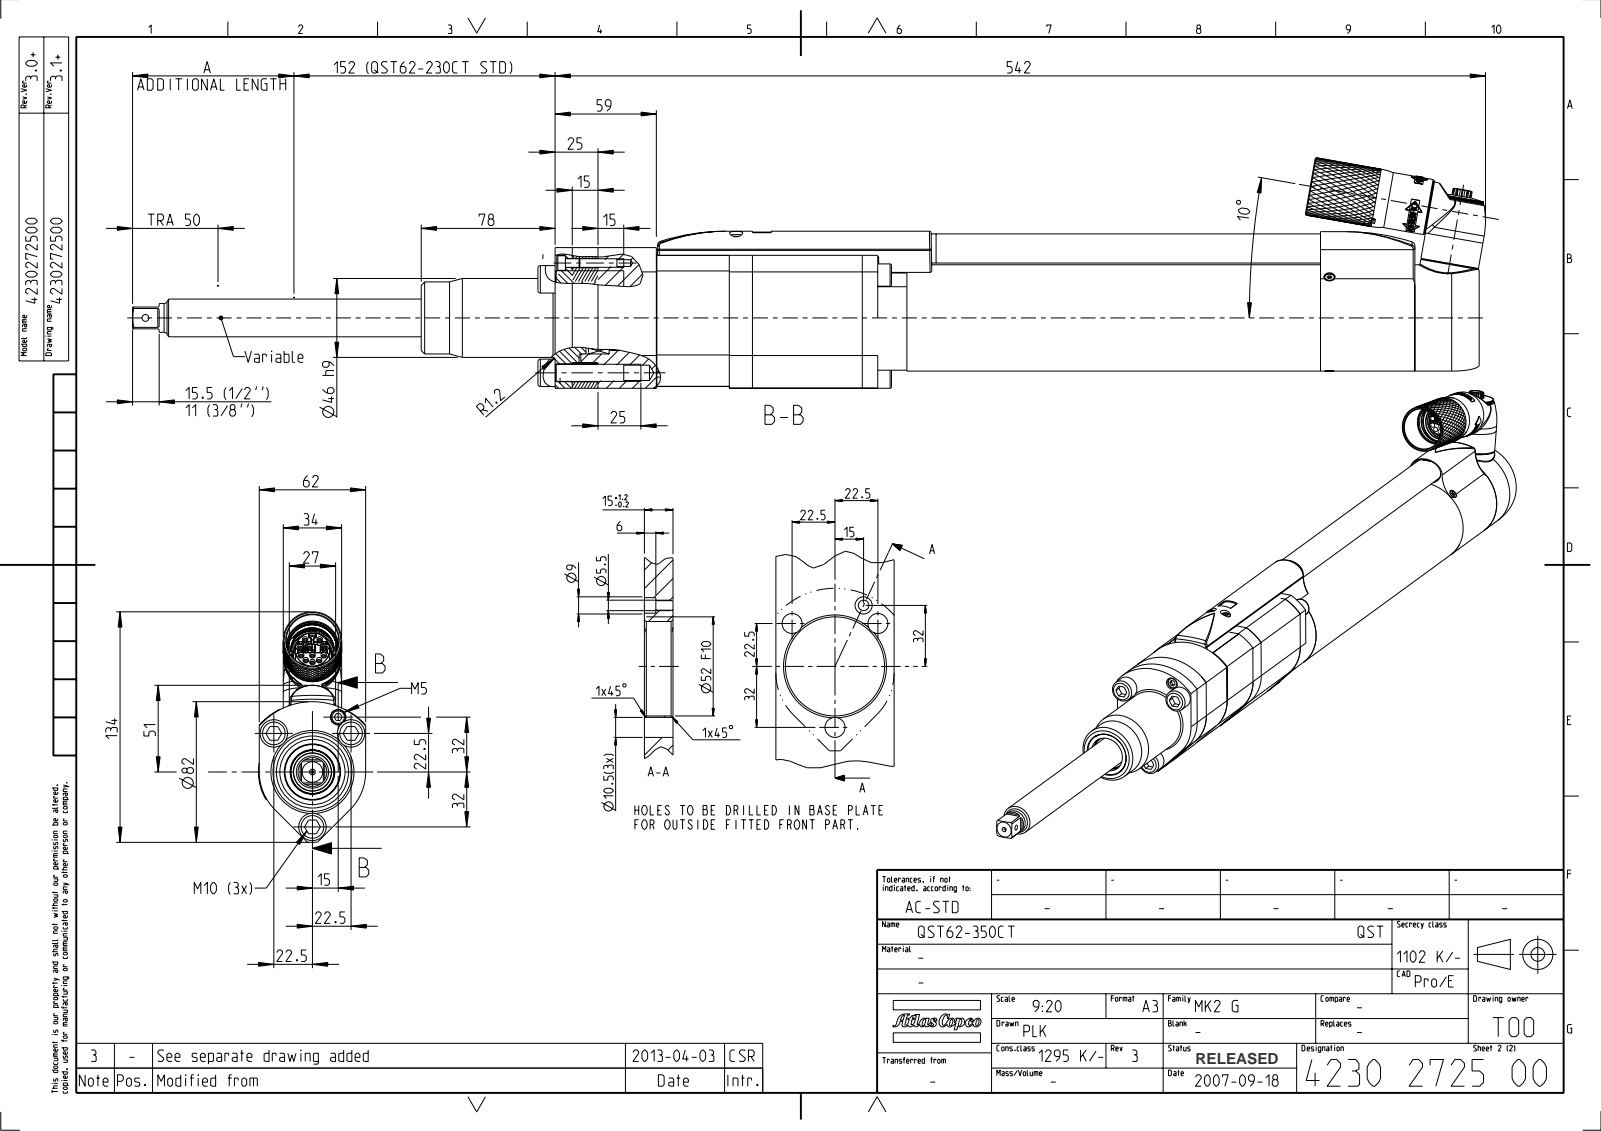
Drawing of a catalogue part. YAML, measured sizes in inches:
part_name: "QST62_REARCOVER_02; QST_CONNECTOR_02; QST62_350_CT_BODY_50; QST62_SPACER_01 (+3 more)"
step_written_by: "PRO/ENGINEER BY PARAMETRIC TECHNOLOGY CORPORATION, 2012420 (CONFIG_CONTROL_DESIGN)"
units: inches
bodies: {solids: 6, faces: 3256, planar: 1268, cylindrical: 1047, other: 941}
overall_size: [31.267, 5.291, 2.441]
volume: 76.95
surface_area: 661.7
round_holes:
  - {diameter: 0.177, count: 8}
  - {diameter: 0.13, count: 7}
  - {diameter: 0.154, count: 4}
  - {diameter: 0.217, count: 4}
  - {diameter: 0.295, count: 4}
  - {diameter: 0.354, count: 4}
  - {diameter: 0.075, count: 3}
  - {diameter: 0.138, count: 3}
  - {diameter: 0.272, count: 3}
  - {diameter: 0.335, count: 3}
  - {diameter: 0.351, count: 3}
  - {diameter: 0.406, count: 3}
round_bosses_or_shafts:
  - {diameter: 0.197, count: 5}
  - {diameter: 0.098, count: 5}
  - {diameter: 1.339, count: 4}
  - {diameter: 0.315, count: 4}
  - {diameter: 0.118, count: 4}
  - {diameter: 0.63, count: 3}
  - {diameter: 0.512, count: 3}
  - {diameter: 0.394, count: 3}
partial_cylinders:
  - {radius: 0.02, count: 49}
  - {radius: 0.008, count: 12}
  - {radius: 0.011, count: 12}
  - {radius: 0.02, count: 12}
  - {radius: 0.039, count: 7}
  - {radius: 0.079, count: 5}
  - {radius: 0.027, count: 4}
  - {radius: 0.047, count: 4}
face_to_face_distances: [2.441, 0.217, 0.591, 0.138, 1.339, 18.74, 0.984, 9.862, 20.217, 20.807]
hole_center_spacings: [0.886, 0.797, 0.582, 0.657, 0.909, 0.91, 1.139, 1.543]
